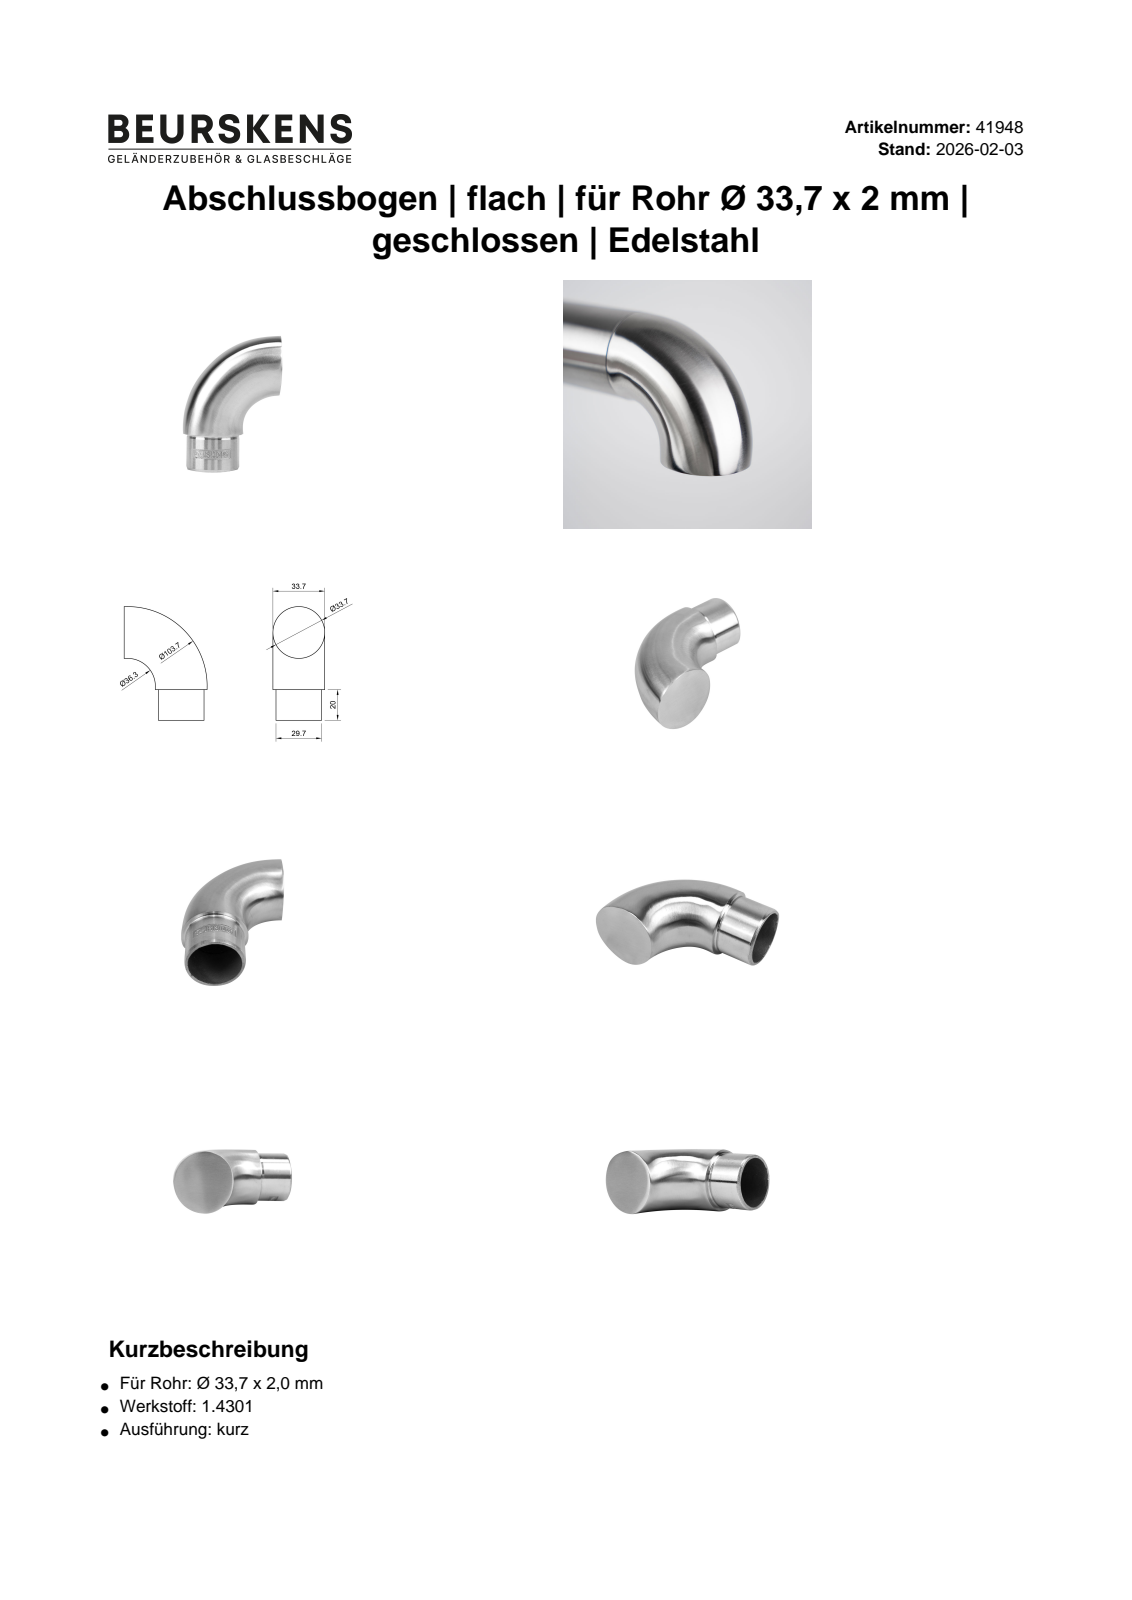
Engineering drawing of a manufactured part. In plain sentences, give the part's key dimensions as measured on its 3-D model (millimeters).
The part is named "41948". Its 3-D file was written by "Autodesk Inventor 2022 (AUTOMOTIVE_DESIGN)". It is 1 solid with 13 faces: 5 planar, 6 cylindrical and 2 other. Overall it measures 74 by 54 by 33.7 millimeters. Its volume is 17 021 cubic millimeters and its surface area 17 208 square millimeters. Round holes: 2 of diameter 29.7, 1 of diameter 25.7. Round bosses or shafts: 2 of diameter 33.7. The main face-to-face distances are 2, 20, 22.
